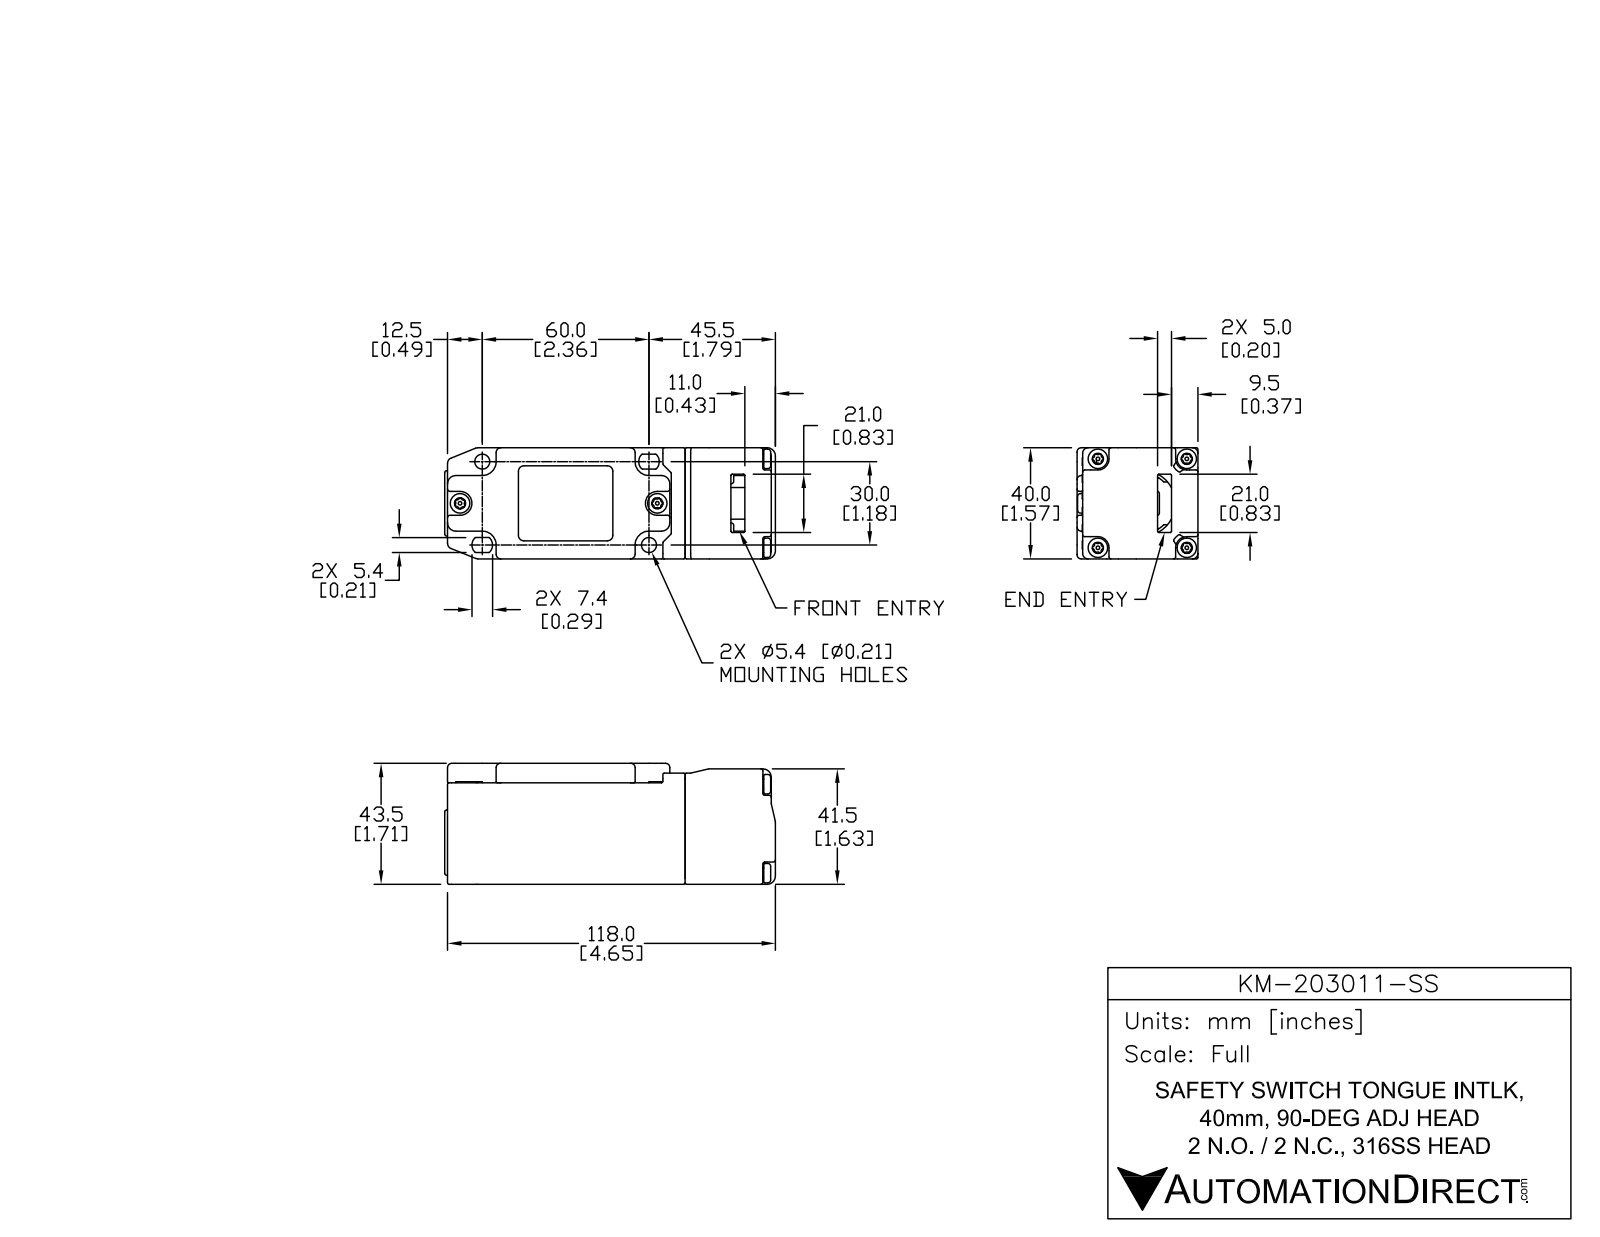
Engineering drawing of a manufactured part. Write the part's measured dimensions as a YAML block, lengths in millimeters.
part_name: "KM-203011-SS"
step_written_by: "SolidWorks 2013 (AUTOMOTIVE_DESIGN)"
units: millimeters
bodies: {solids: 1, faces: 581, planar: 128, cylindrical: 263, other: 190}
overall_size: [119.63, 43.56, 40]
volume: 183300
surface_area: 28465
round_holes:
  - {diameter: 5.4, count: 2}
round_bosses_or_shafts:
  - {diameter: 6.77, count: 4}
  - {diameter: 6.63, count: 2}
  - {diameter: 23, count: 1}
  - {diameter: 5.6, count: 1}
partial_cylinders:
  - {radius: 0.5, count: 95}
  - {radius: 0.25, count: 68}
  - {radius: 3, count: 5}
  - {radius: 1.45, count: 4}
  - {radius: 1.7, count: 4}
  - {radius: 2.75, count: 4}
  - {radius: 4, count: 4}
  - {radius: 5, count: 4}
face_to_face_distances: [40, 43.5, 0.5, 43, 118, 2.6, 5, 9.5, 102, 16]
hole_center_spacings: [67.08]
